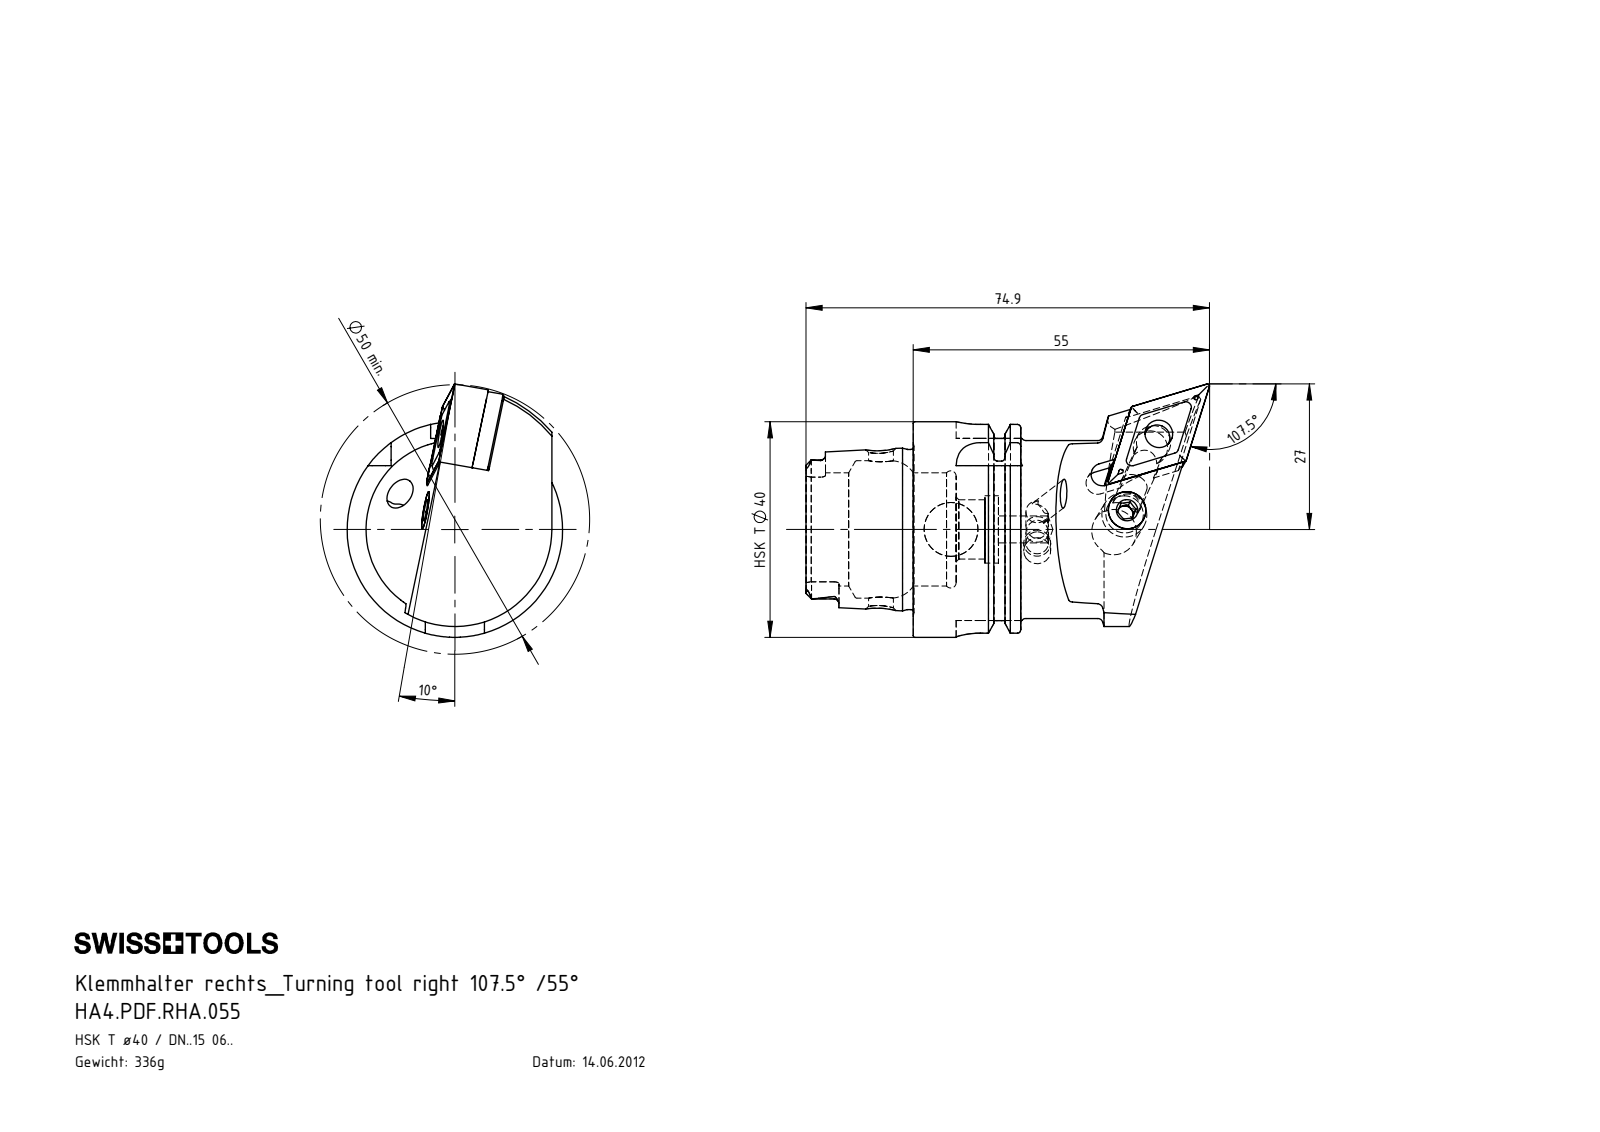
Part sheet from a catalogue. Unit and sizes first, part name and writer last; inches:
Units: inches
Overall size (bounding box): 2.949 × 1.85 × 1.575
Round holes (diameter × count): ⌀0.165 ×2, ⌀0.197 ×2, ⌀0.157 ×1, ⌀0.181 ×1, ⌀0.203 ×1, ⌀0.252 ×1, ⌀0.276 ×1, ⌀0.331 ×1, ⌀0.394 ×1, ⌀0.433 ×1, ⌀0.492 ×1, ⌀0.827 ×1
Round bosses / shafts (diameter × count): ⌀1.575 ×1, ⌀1.368 ×1, ⌀1.299 ×1, ⌀1.17 ×1, ⌀0.315 ×1, ⌀0.311 ×1, ⌀0.252 ×1, ⌀0.197 ×1
Partial cylindrical surfaces — rounded edges, fillets, slot ends (radius × count): R0.035 ×6, R0.016 ×4, R0.039 ×4, R0.074 ×4, R0.177 ×4, R0.098 ×2, R0.031 ×1, R0.083 ×1
Main face-to-face distances: 0.237, 0.5, 0.484, 0.313, 0.785, 0.472, 0.362, 0.191, 0.484, 0.125
Hole centre spacings: 0.613, 0.613
Volume: 2.67 in³ · Surface area: 26.08 in²
Bodies: 8 solids, 378 faces (118 planar, 103 cylindrical, 157 other)
Part name (STEP PRODUCT): HA4-PDF.RHA.055; WDF-ER2.101.003_A; WCD-ER4.101.017_A; WCD-ER1.101.000 (+4 more)
STEP written by: SolidWorks 2012 (CONFIG_CONTROL_DESIGN)
